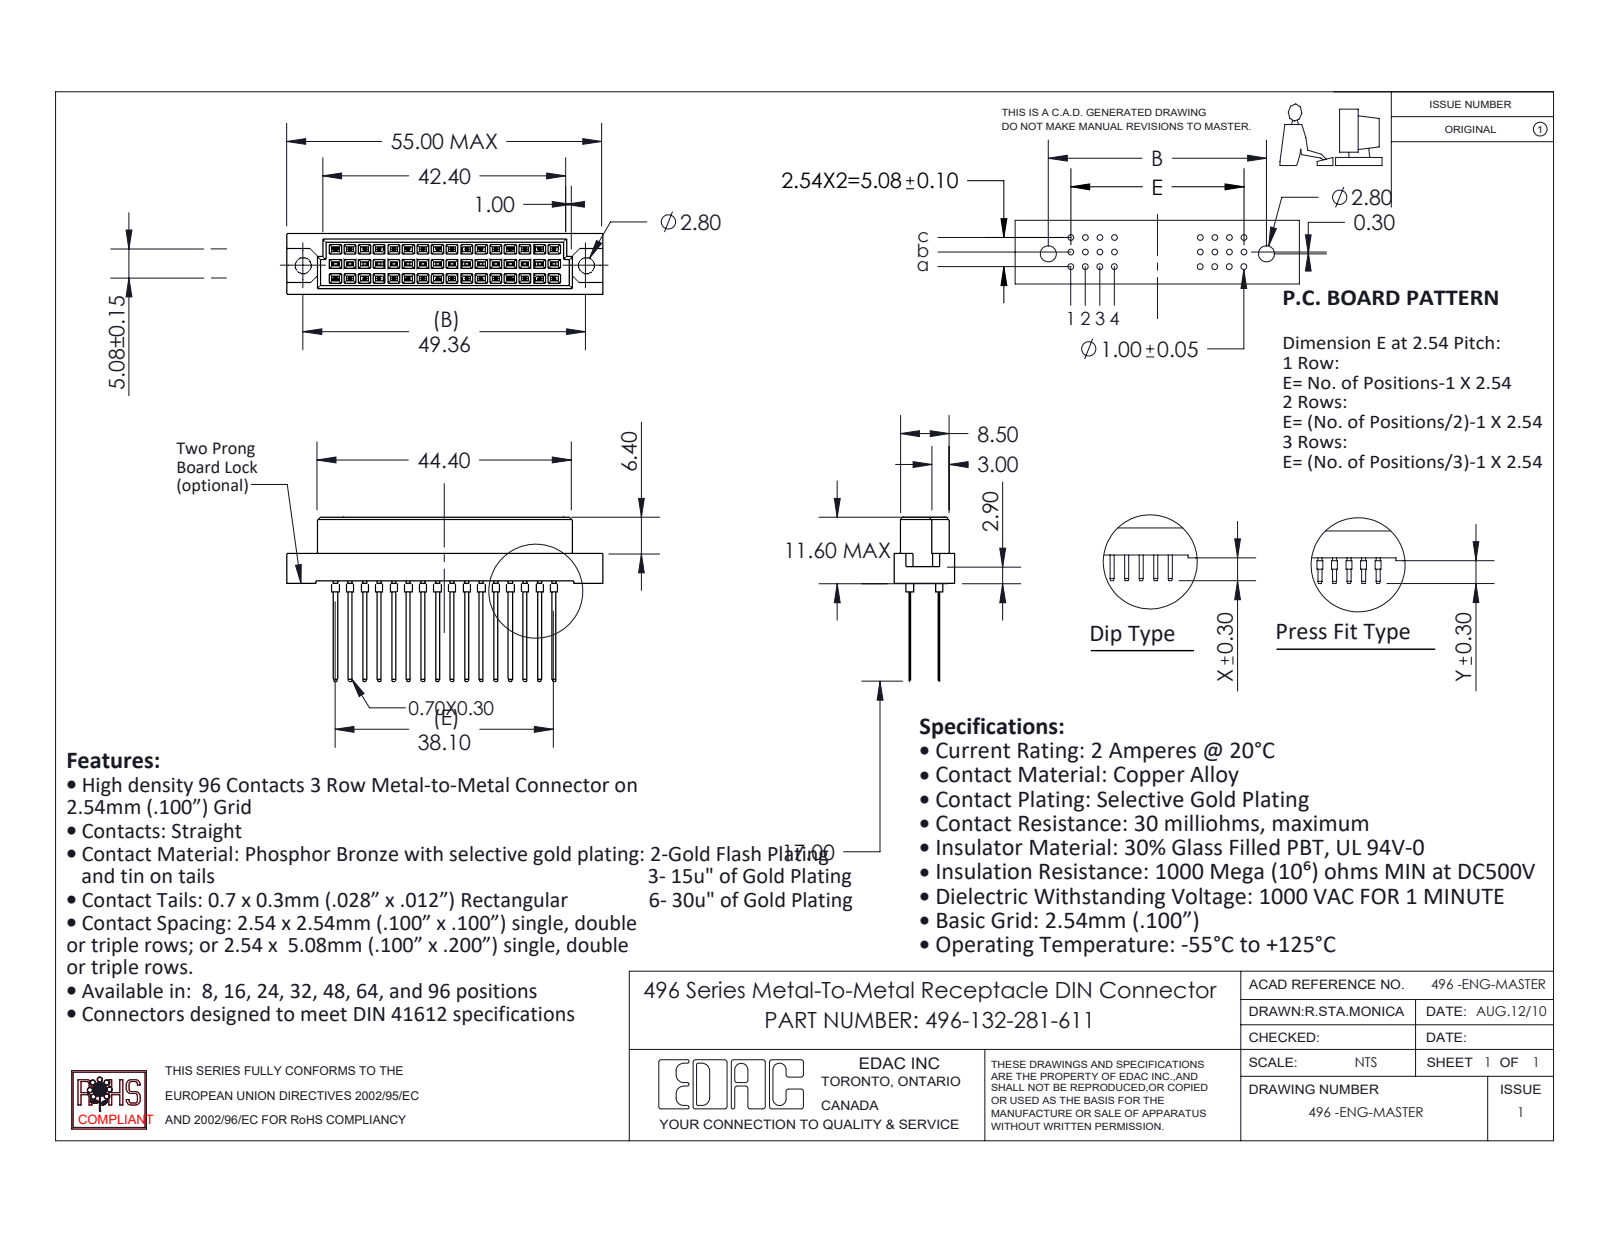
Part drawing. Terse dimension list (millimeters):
name: 496 Part_48; 496-132-281-611; 496-290_81
written by: SolidWorks 2020 (CONFIG_CONTROL_DESIGN)
unit: mm
bodies: 33 solids, 1242 faces (1174 planar, 68 cylindrical, 0 other)
size: 55 × 28.6 × 10.6
volume: 4 759 mm³; area: 5 672 mm²
holes: 2× ⌀2.8
bosses: 32× ⌀1
face distances: 5.08, 2.54, 2.61, 2.91, 7.69, 7.99, 1.05, 9.55, 1.56, 1.86
hole spacings: 49.36
